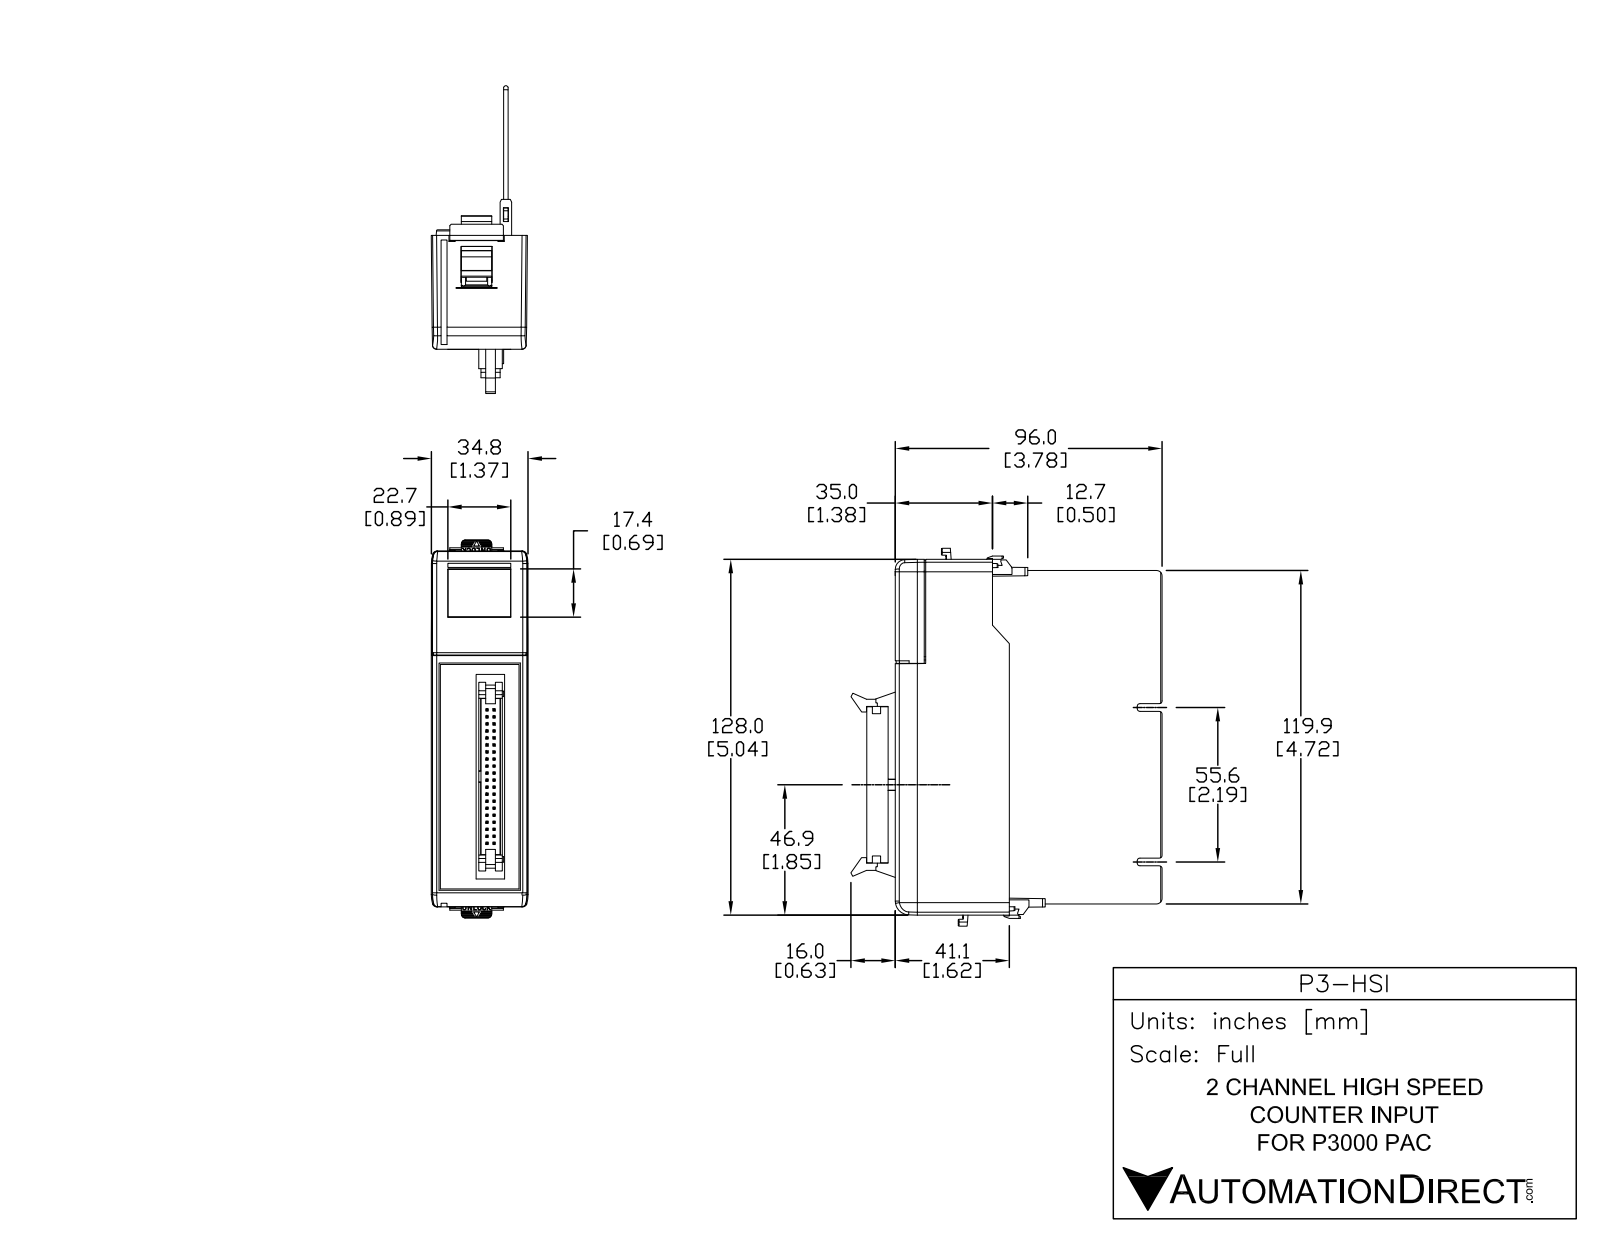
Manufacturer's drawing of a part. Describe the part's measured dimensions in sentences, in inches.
The part is named "P3-HSI". Its 3-D file was written by "SolidWorks 2012 (AUTOMOTIVE_DESIGN)". It is 1 solid with 1491 faces: 1374 planar, 52 cylindrical and 65 other. Overall it measures 5.358 by 4.405 by 1.37 inches. Its volume is 11.62 cubic inches and its surface area 68.61 square inches. Partial cylindrical surfaces (rounded edges, fillets, slot ends): 16 of radius 0.039, 10 of radius 0.012, 6 of radius 0.059, 2 of radius 0.004, 2 of radius 0.02, 2 of radius 0.045, 2 of radius 0.047, 2 of radius 0.079. The main face-to-face distances are 0.063, 1.623, 0.051, 0.114, 0.24, 1.383, 0.323, 0.303, 0.272, 0.386.
